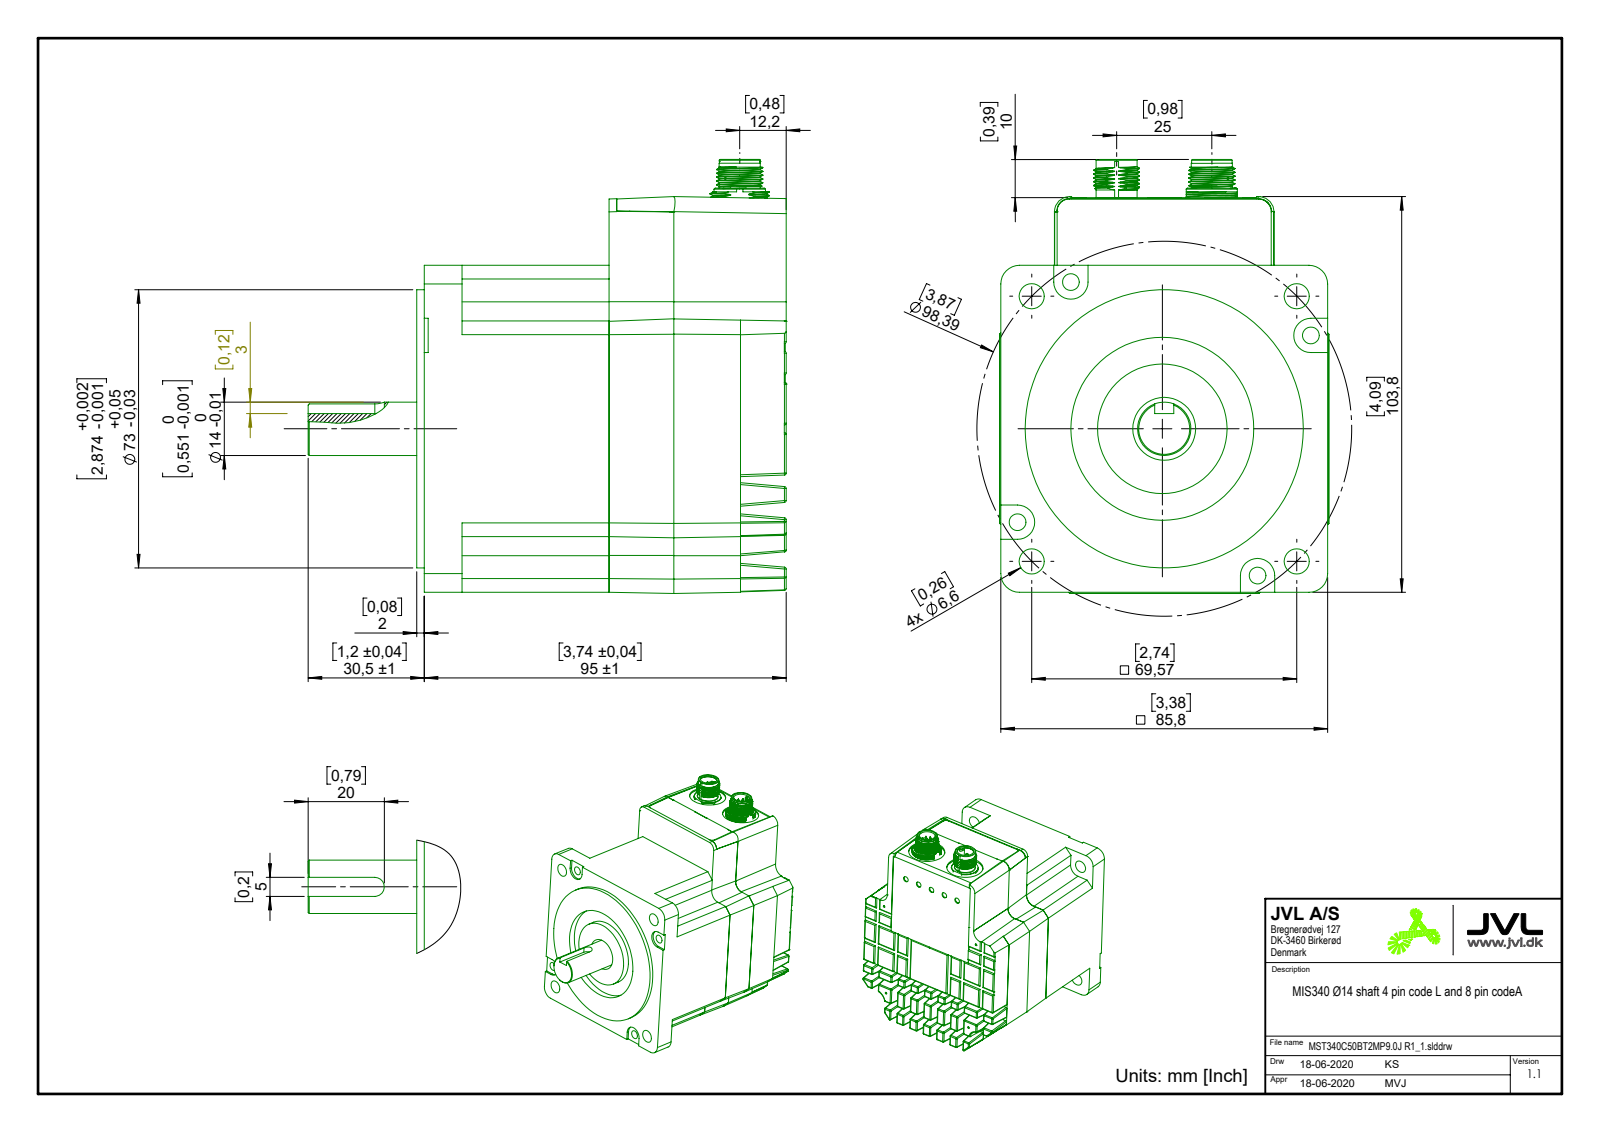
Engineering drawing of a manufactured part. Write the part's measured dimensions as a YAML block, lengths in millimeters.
part_name: "MST340C50BT2MP9.0J R1_1"
step_written_by: "SolidWorks 2018 (AUTOMOTIVE_DESIGN)"
units: millimeters
bodies: {solids: 1, faces: 1299, planar: 416, cylindrical: 540, other: 343}
overall_size: [125.5, 113.87, 86.41]
volume: 654579
surface_area: 85692
round_holes:
  - {diameter: 1, count: 12}
  - {diameter: 1.1, count: 8}
  - {diameter: 3, count: 5}
  - {diameter: 4.3, count: 4}
  - {diameter: 4.4, count: 4}
  - {diameter: 6.6, count: 4}
  - {diameter: 19, count: 2}
  - {diameter: 1.7, count: 1}
  - {diameter: 8.2, count: 1}
  - {diameter: 8.85, count: 1}
  - {diameter: 8.9, count: 1}
  - {diameter: 16, count: 1}
round_bosses_or_shafts:
  - {diameter: 0.85, count: 8}
  - {diameter: 0.8, count: 8}
  - {diameter: 1.5, count: 4}
  - {diameter: 73, count: 1}
  - {diameter: 34, count: 1}
  - {diameter: 14, count: 1}
  - {diameter: 13.5, count: 1}
  - {diameter: 12.1, count: 1}
partial_cylinders:
  - {radius: 0.5, count: 167}
  - {radius: 0.1, count: 11}
  - {radius: 0.2, count: 4}
  - {radius: 0.4, count: 4}
  - {radius: 4.5, count: 4}
  - {radius: 4.9, count: 4}
  - {radius: 5, count: 4}
  - {radius: 9.5, count: 4}
face_to_face_distances: [85.8, 0.6, 50.5, 51.1, 2, 48.5, 49.1, 14.6, 45.9, 97]
hole_center_spacings: [2.75, 2.74, 2.32, 8.4, 45.63, 64.54, 69.57, 4.21]
